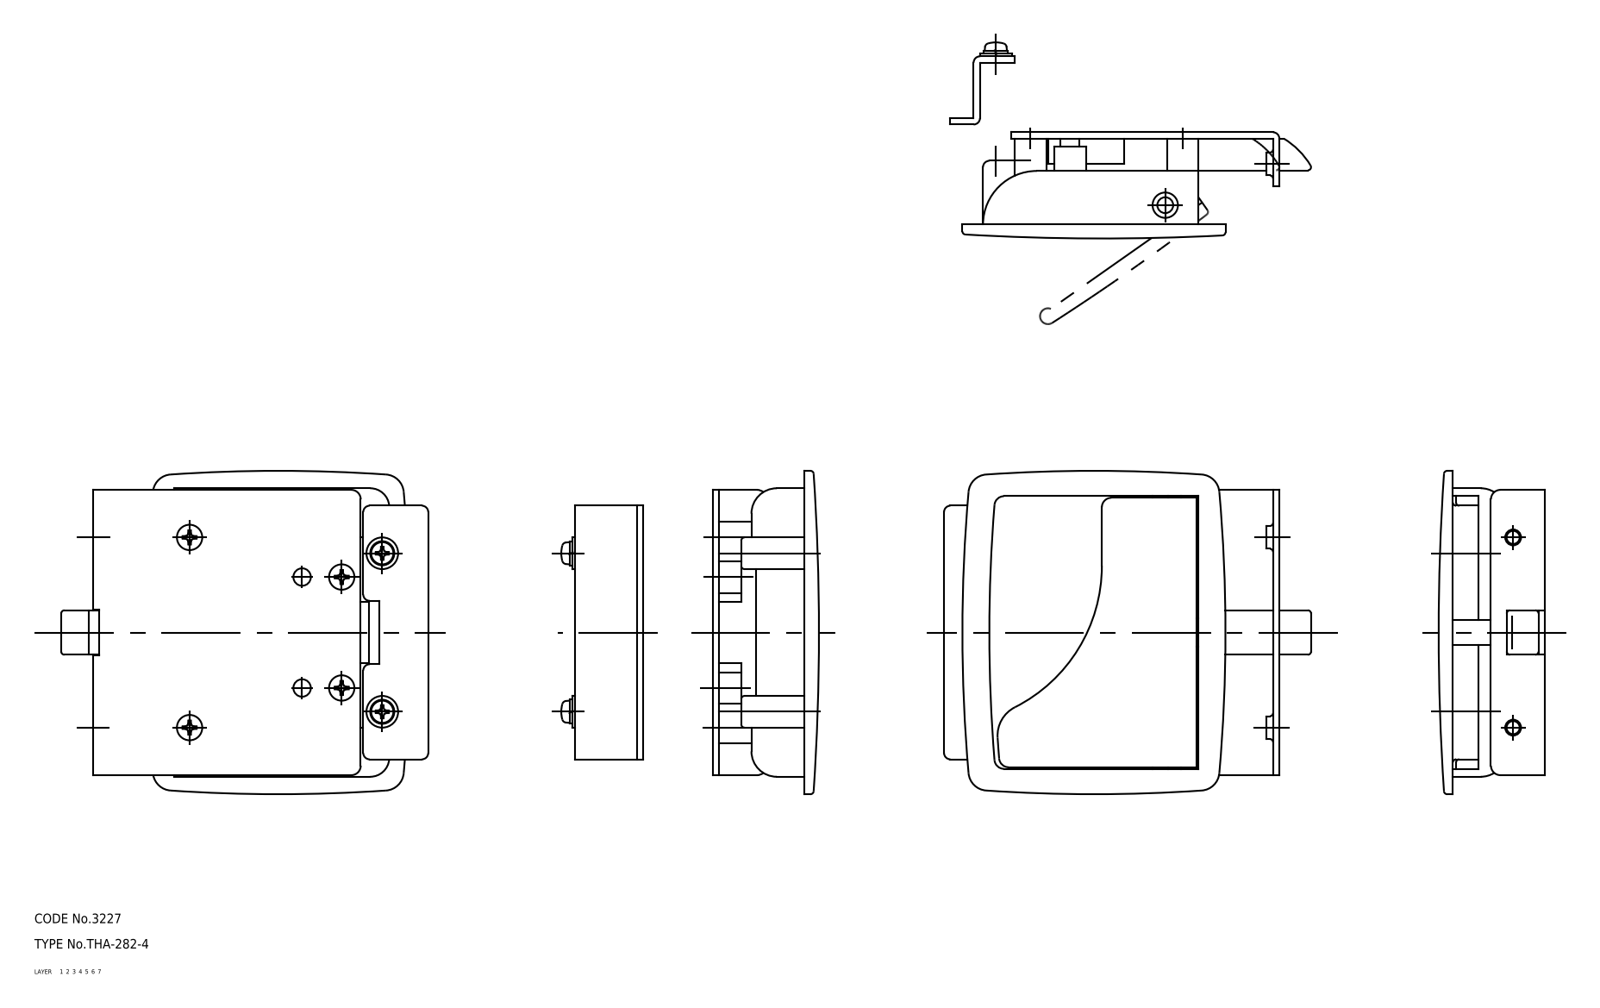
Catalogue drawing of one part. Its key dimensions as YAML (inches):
part_name: "screw_mr; bracket_B_mr; handle_mr; latch_mr (+3 more)"
step_written_by: "CADfix (AUTOMOTIVE_DESIGN)"
units: inches
bodies: {solids: 7, faces: 534, planar: 0, cylindrical: 0, other: 534}
overall_size: [4.508, 4.016, 1.319]
volume: 5.567
surface_area: 110.3
